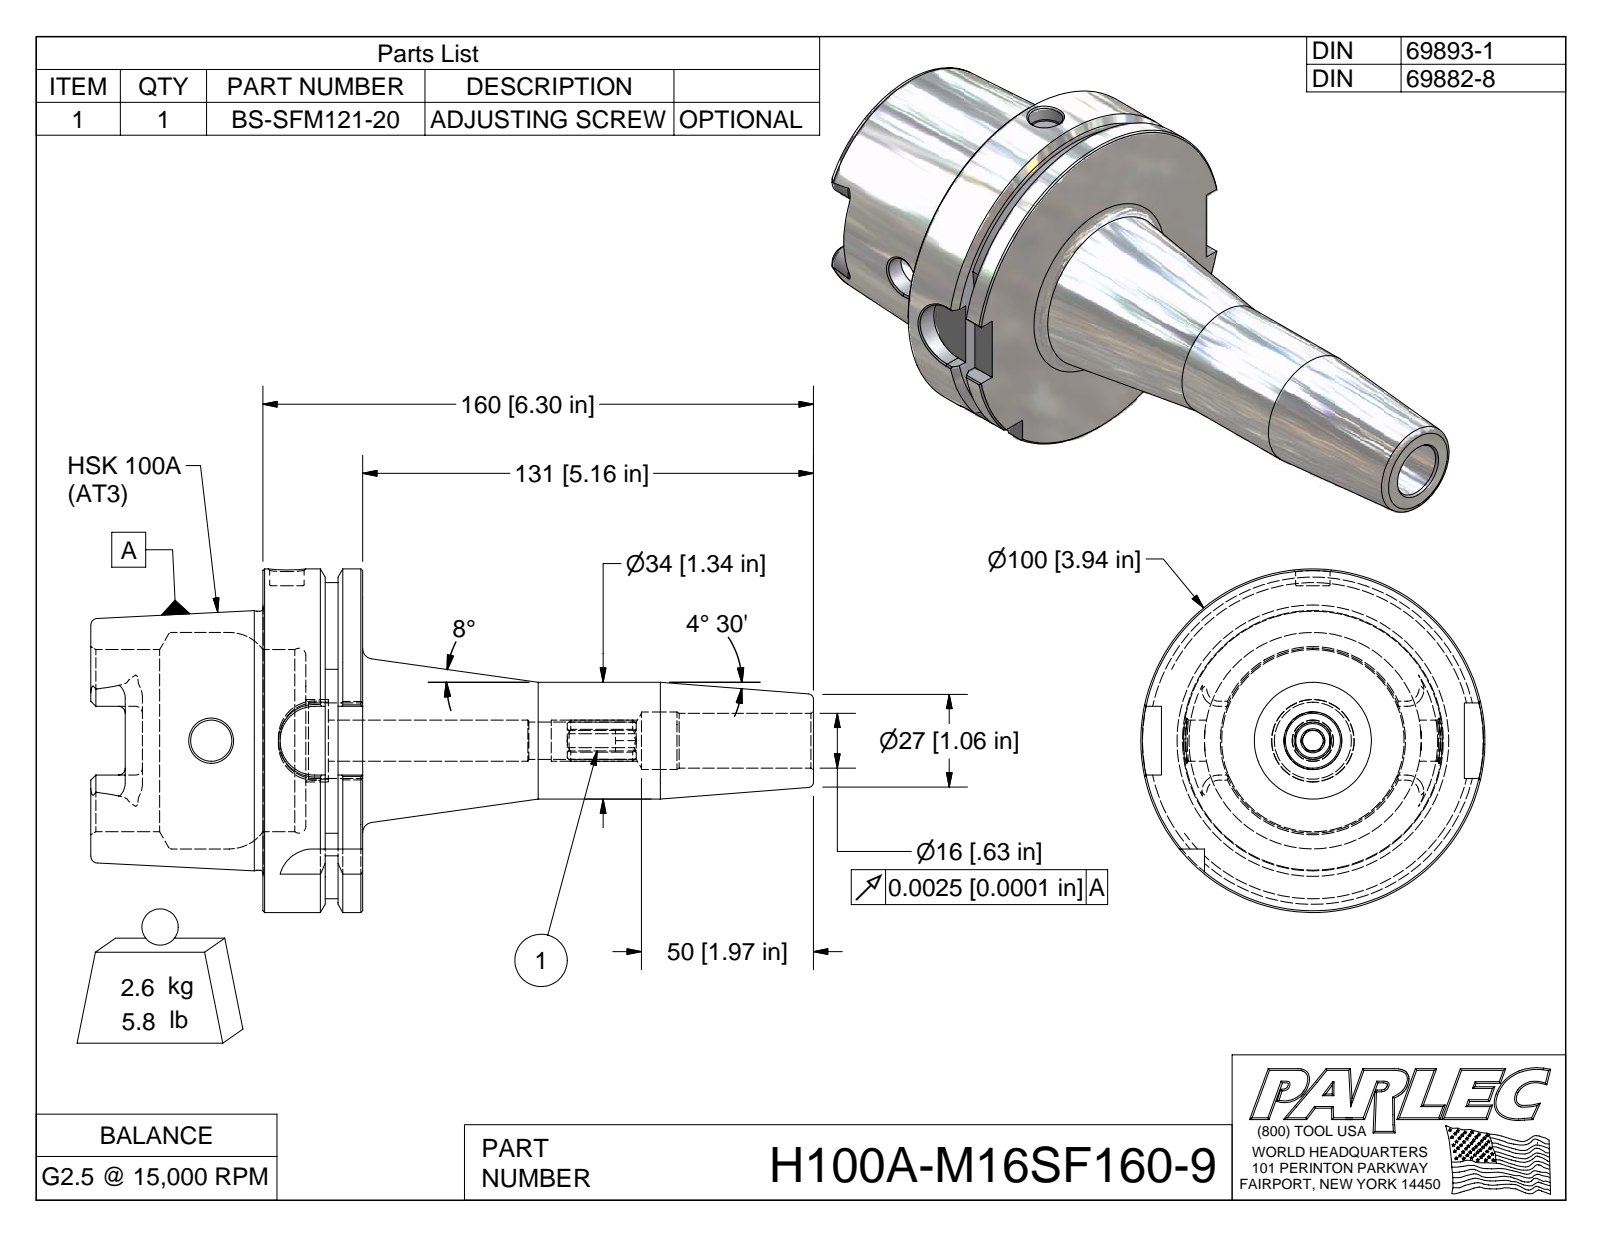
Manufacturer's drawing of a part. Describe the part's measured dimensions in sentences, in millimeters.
The part is named "H100A-M16SF160-9; H100A-M16SF160-9-1; BS-SFM121-20". Its 3-D file was written by "Autodesk Inventor 2009 (AUTOMOTIVE_DESIGN)". It is 2 solids with 148 faces: 48 planar, 29 cylindrical and 71 other. Overall it measures 210 by 100 by 100 millimeters. Its volume is 373 000 cubic millimeters and its surface area 69 350 square millimeters. Round holes: 1 of diameter 10, 1 of diameter 12, 1 of diameter 16, 1 of diameter 16.7, 1 of diameter 22.4, 1 of diameter 53, 1 of diameter 63. Round bosses or shafts: 1 of diameter 100, 1 of diameter 75.4, 1 of diameter 34. Partial cylindrical surfaces (rounded edges, fillets, slot ends): 4 of radius 10, 3 of radius 2, 2 of radius 4.9, 1 of radius 6, 1 of radius 46. The main face-to-face distances are 29, 12.5, 16.5, 50, 62.5, 79, 68.1, 18.1, 5.6, 10.9.
